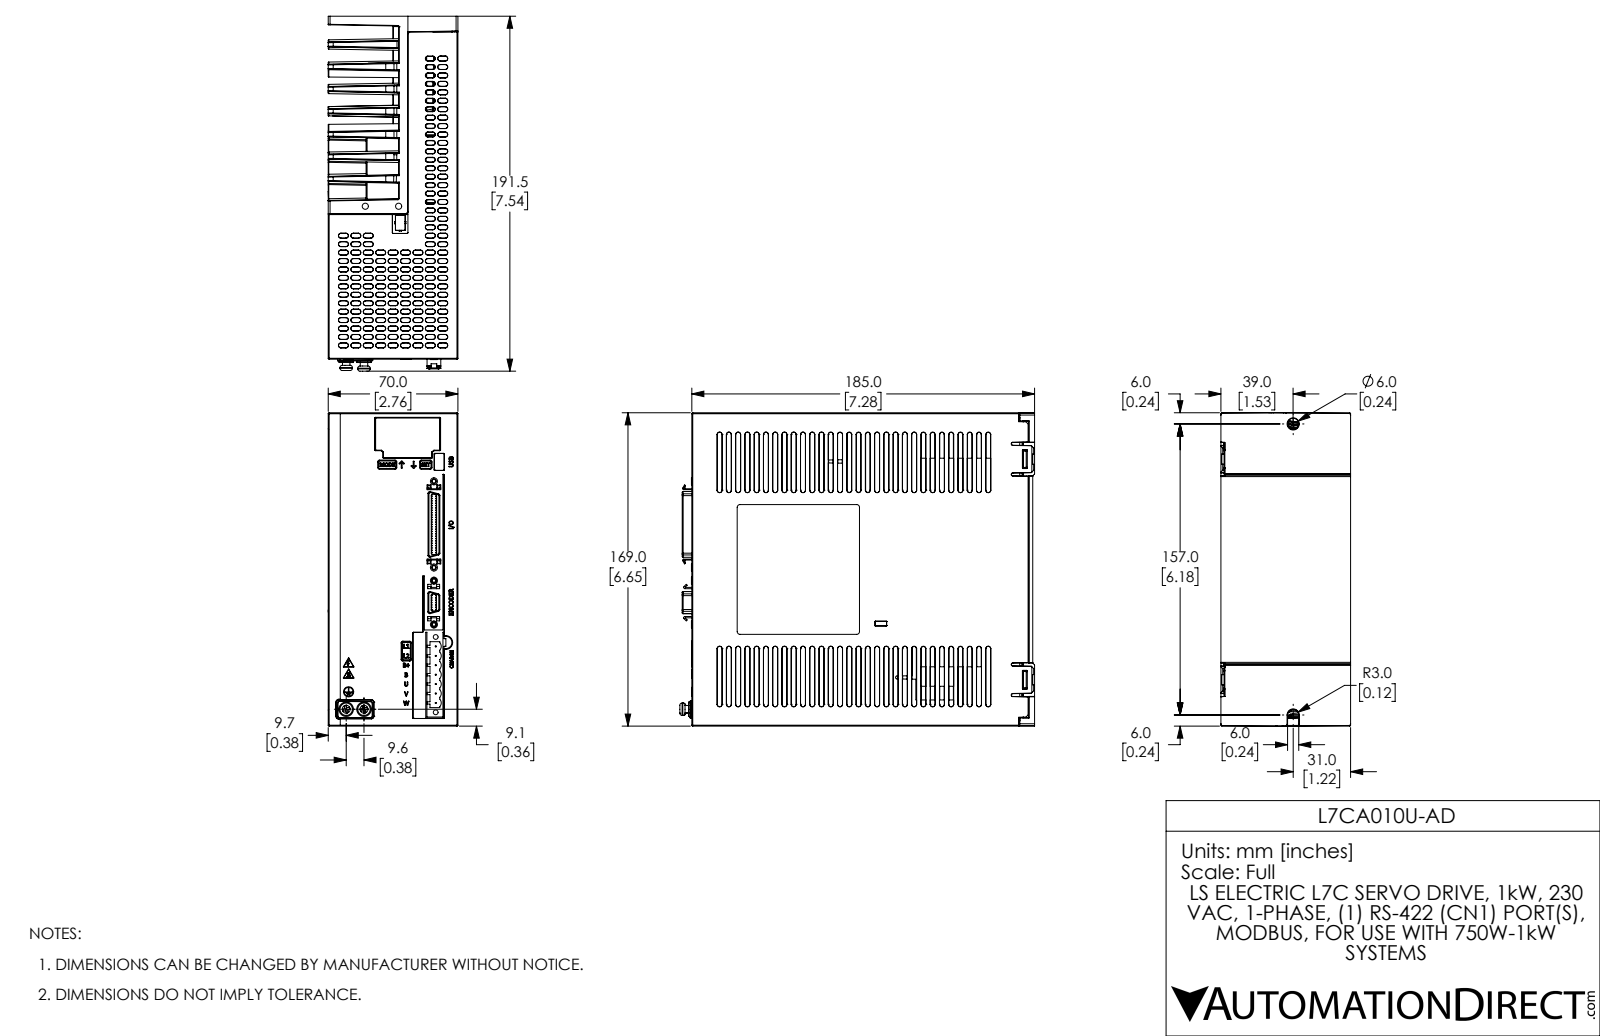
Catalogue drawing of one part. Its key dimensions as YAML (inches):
part_name: "L7C 200V (750W,1kW) R1 wo Heatsink 1 wowash 1 ext3A redonly1c2 COMPLETE 3B NEW"
step_written_by: "SolidWorks 2017 (AUTOMOTIVE_DESIGN)"
units: inches
bodies: {solids: 6, faces: 6167, planar: 2756, cylindrical: 1161, other: 2250}
overall_size: [7.538, 6.654, 2.949]
volume: 95.34
surface_area: 467.5
round_holes:
  - {diameter: 0.098, count: 11}
  - {diameter: 0.13, count: 6}
  - {diameter: 0.102, count: 4}
  - {diameter: 0.157, count: 1}
round_bosses_or_shafts:
  - {diameter: 0.15, count: 4}
  - {diameter: 0.307, count: 2}
  - {diameter: 0.264, count: 2}
  - {diameter: 0.157, count: 1}
  - {diameter: 0.11, count: 1}
  - {diameter: 0.098, count: 1}
partial_cylinders:
  - {radius: 0.012, count: 383}
  - {radius: 0.02, count: 164}
  - {radius: 0.039, count: 72}
  - {radius: 0.016, count: 32}
  - {radius: 0.008, count: 29}
  - {radius: 0.118, count: 22}
  - {radius: 0.079, count: 12}
  - {radius: 0.005, count: 6}
face_to_face_distances: [0.472, 0.945, 2.756, 1.909, 0.319, 2.437, 1.437, 2.5, 0.063, 0.256]
hole_center_spacings: [1.26, 1.781, 0.268, 0.378, 0.433, 0.443, 0.709, 0.787]
